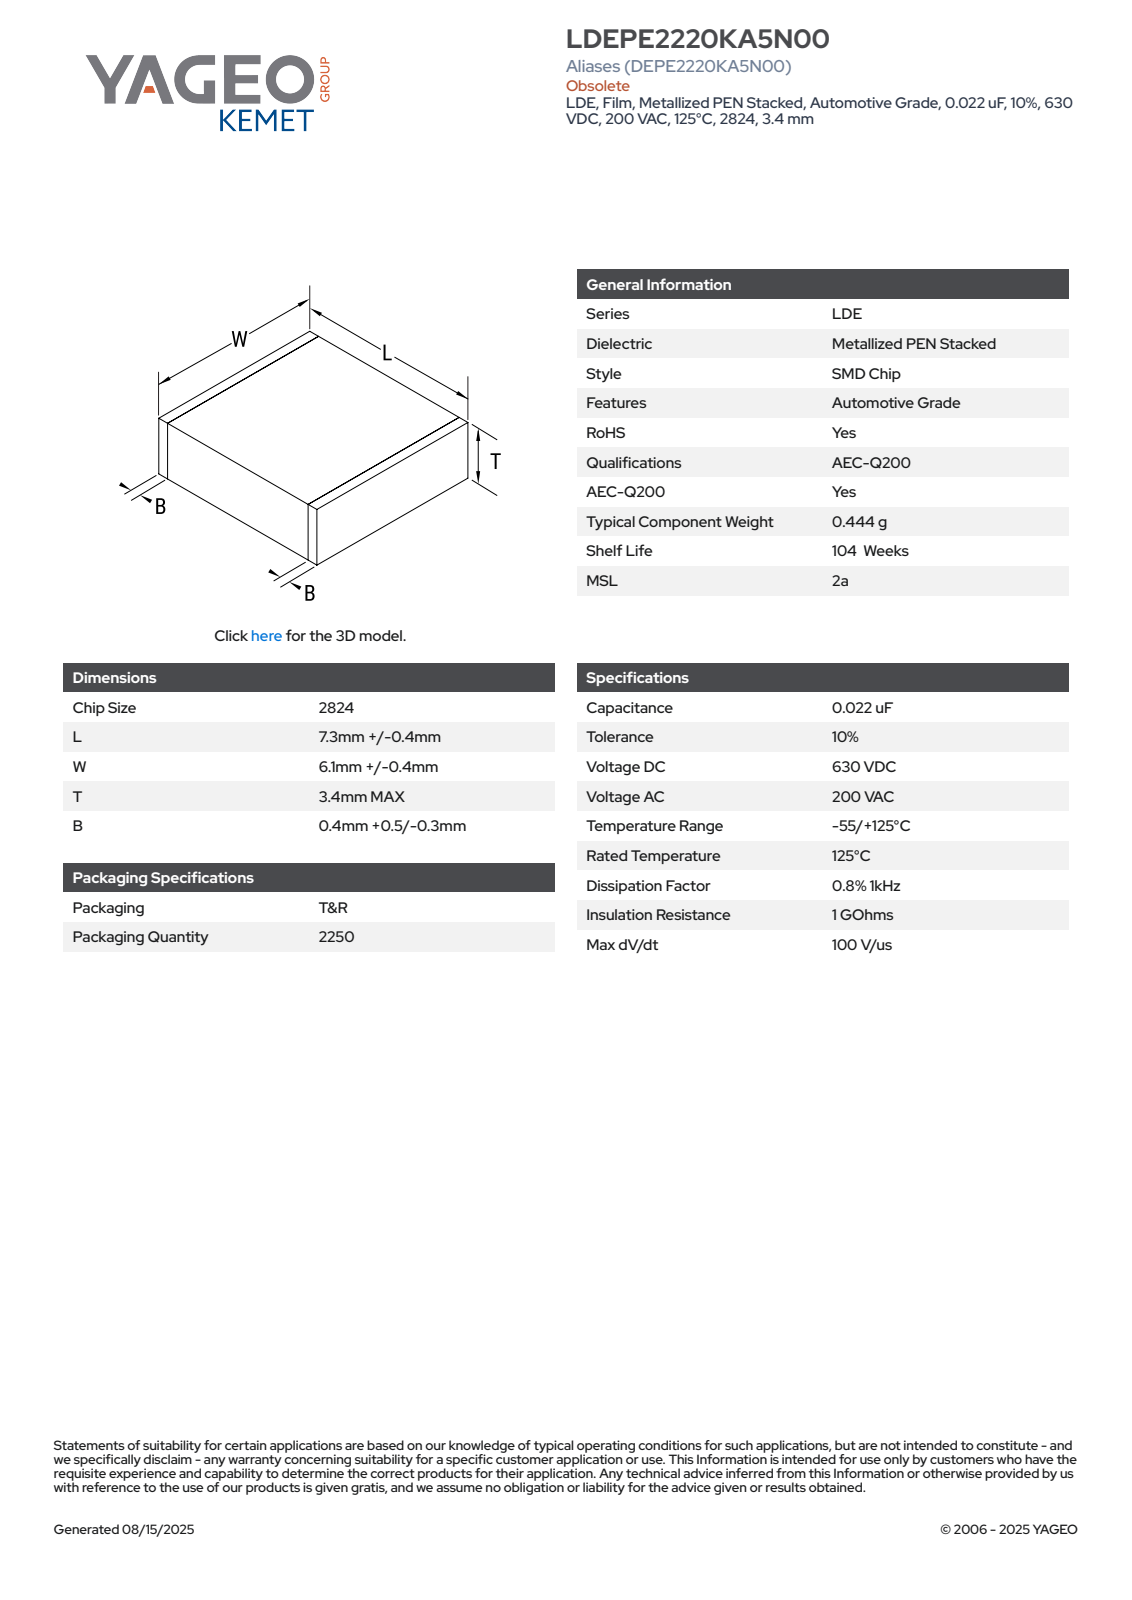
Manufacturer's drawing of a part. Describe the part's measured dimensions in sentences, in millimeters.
The part is named "CFS_LDELDB_2824_L7.7W6.5T3.4B0.9". Its 3-D file was written by "SolidWorks 2020 (AUTOMOTIVE_DESIGN)". It is 4 solids with 73 faces: 73 planar, 0 cylindrical and 0 other. Overall it measures 7.7 by 6.5 by 3.4 millimeters. Its volume is 169 cubic millimeters and its surface area 199 square millimeters. The main face-to-face distances are 3.38, 6.48, 7.7, 3.39, 6.49, 3.4, 6.5, 0.5, 7.2, 6.7.
